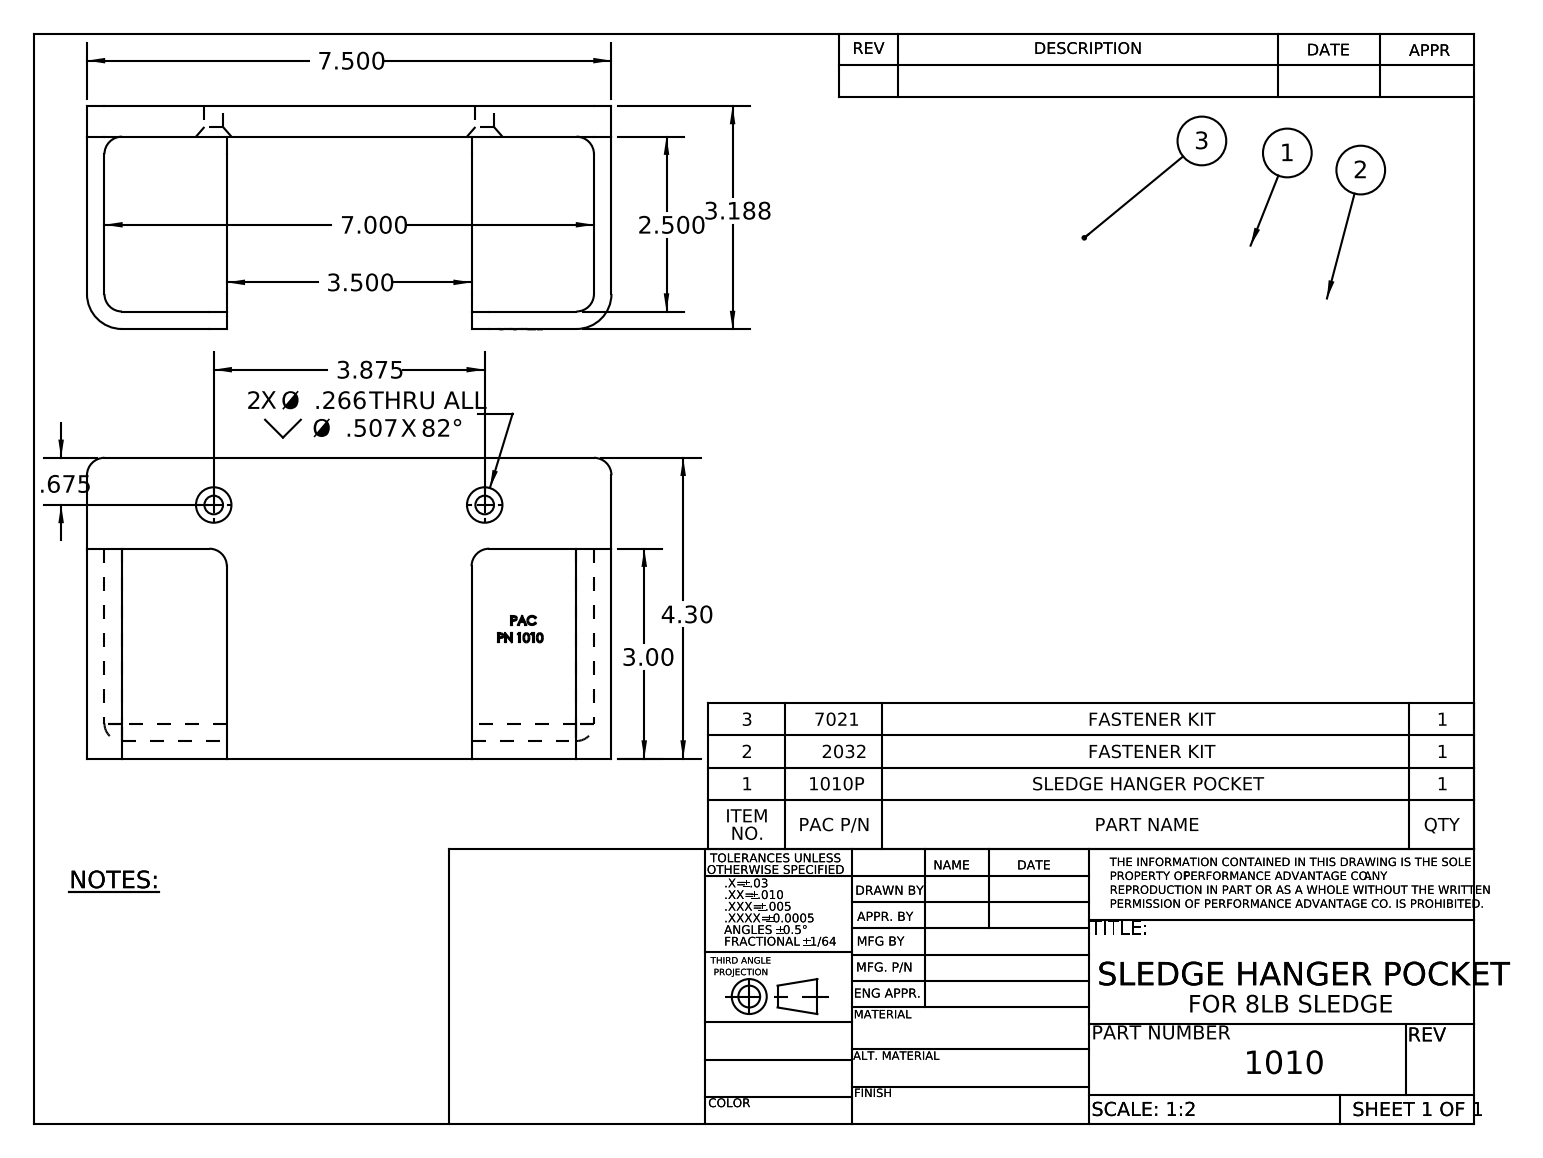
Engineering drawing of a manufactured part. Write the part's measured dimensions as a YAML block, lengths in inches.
part_name: "1010"
step_written_by: "SolidWorks 2010 (CONFIG_CONTROL_DESIGN)"
units: inches
bodies: {solids: 1, faces: 150, planar: 83, cylindrical: 20, other: 47}
overall_size: [7.5, 4.3, 3.193]
volume: 22.94
surface_area: 145.4
round_holes:
  - {diameter: 0.266, count: 2}
partial_cylinders:
  - {radius: 0.25, count: 12}
  - {radius: 0.5, count: 2}
face_to_face_distances: [0.437, 0.25, 2.75, 7.25, 3.187, 7.5, 2.937, 2.5, 7, 4.3]
hole_center_spacings: [3.875]
